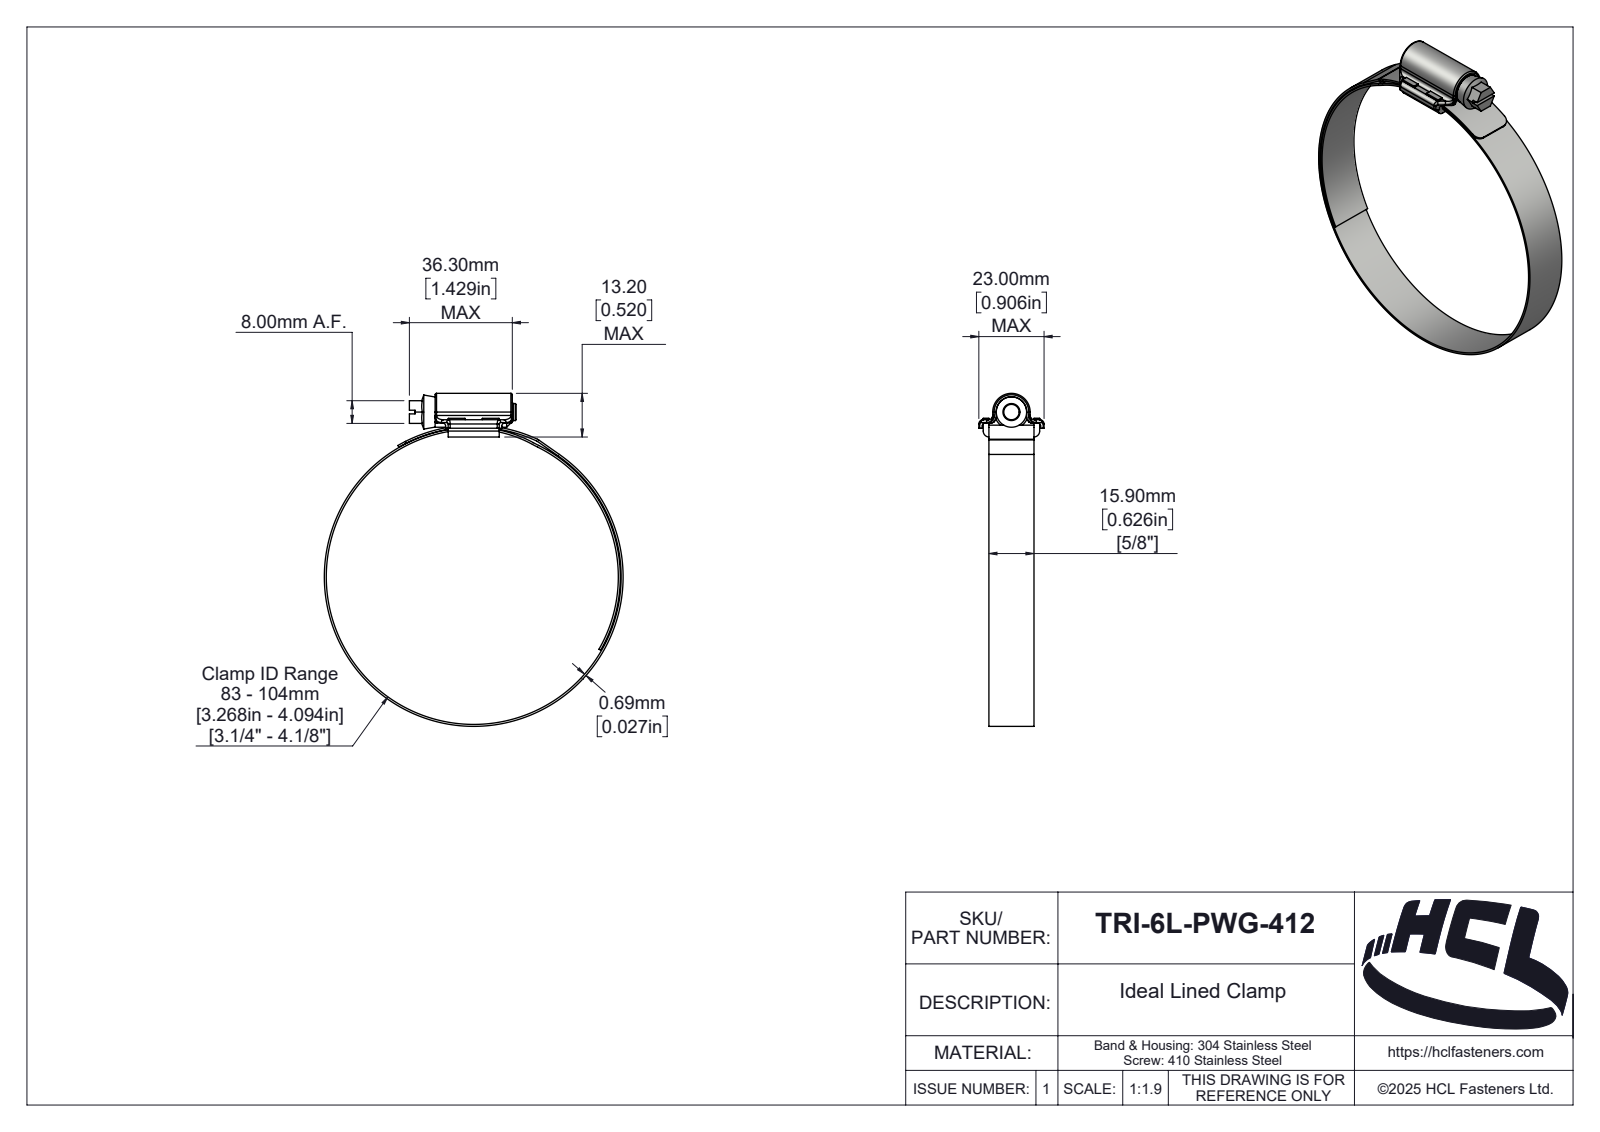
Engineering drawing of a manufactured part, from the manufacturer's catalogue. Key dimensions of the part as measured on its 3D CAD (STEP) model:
Part name (STEP PRODUCT): TRI-6L-PWG-412
STEP written by: SolidWorks 2025 (AUTOMOTIVE_DESIGN)
Units: millimetres
Bodies: 4 solids, 268 faces (87 planar, 102 cylindrical, 79 other)
Overall size (bounding box): 117.39 × 105.38 × 23
Volume: 10 293 mm³ · Surface area: 20 029 mm²
Round holes (diameter × count): ⌀104 ×1
Round bosses / shafts (diameter × count): ⌀105.38 ×1, ⌀10.7 ×1, ⌀6 ×1
Partial cylindrical surfaces — rounded edges, fillets, slot ends (radius × count): R1 ×14, R0.5 ×4, R1.5 ×4, R2 ×3, R0.1 ×2, R2.1 ×2, R3 ×2, R0.46 ×1
Main face-to-face distances: 2, 15.9, 17.9, 4.9, 0.69, 1.2, 4.55, 3.35, 15.35, 2.55
